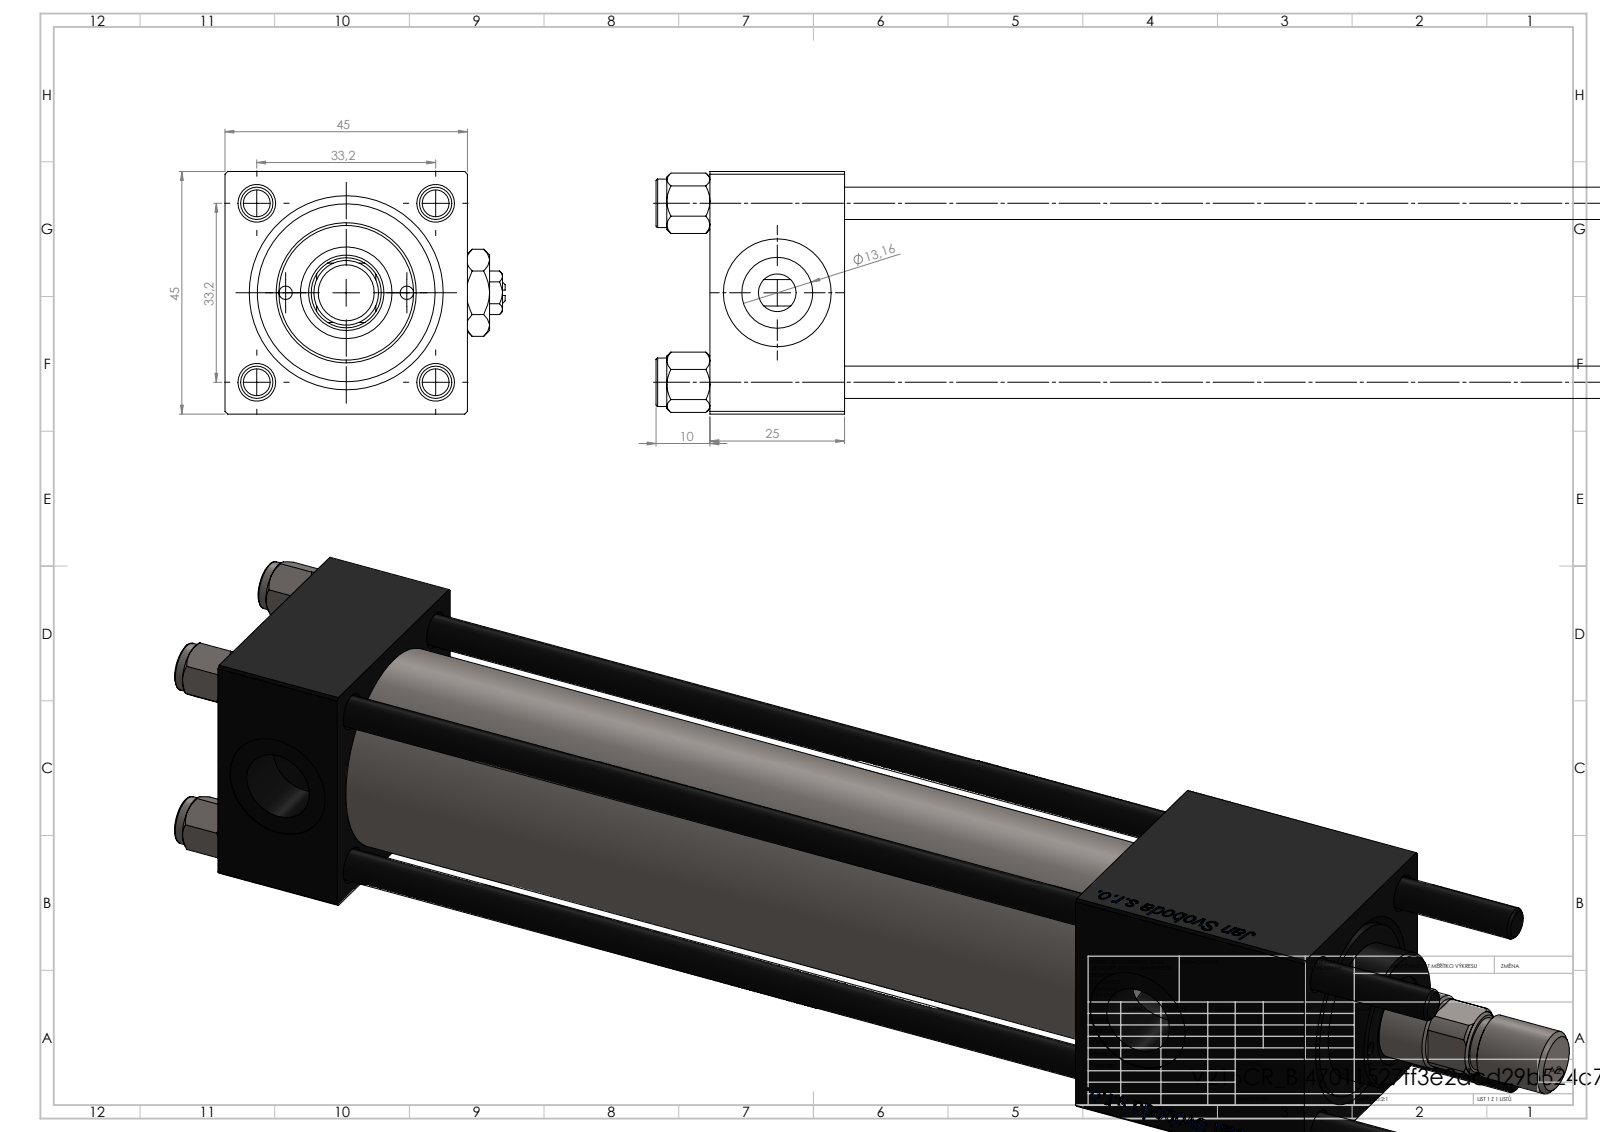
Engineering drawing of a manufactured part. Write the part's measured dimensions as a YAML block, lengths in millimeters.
part_name: "V215_VC_A; NUT_M5_B; V215CR_B-1; V215CR_B_TYCINKA (+3 more)"
step_written_by: "SolidWorks 2019 (CONFIG_CONTROL_DESIGN)"
units: millimeters
bodies: {solids: 13, faces: 1228, planar: 460, cylindrical: 92, other: 676}
overall_size: [279, 52, 45]
volume: 261796
surface_area: 110330
round_holes:
  - {diameter: 6, count: 4}
  - {diameter: 2.5, count: 2}
  - {diameter: 7, count: 2}
  - {diameter: 13.16, count: 2}
  - {diameter: 20, count: 2}
  - {diameter: 6.5, count: 1}
  - {diameter: 14, count: 1}
  - {diameter: 17, count: 1}
  - {diameter: 24, count: 1}
  - {diameter: 32, count: 1}
  - {diameter: 33, count: 1}
round_bosses_or_shafts:
  - {diameter: 9, count: 4}
  - {diameter: 38, count: 1}
  - {diameter: 26, count: 1}
  - {diameter: 12, count: 1}
  - {diameter: 10, count: 1}
partial_cylinders:
  - {radius: 6.5, count: 1}
face_to_face_distances: [45, 25, 228, 203, 180, 155, 48, 199.3, 174.3, 19.3]
hole_center_spacings: [17.44, 23.48, 32.42, 33.2, 11.25, 46.95, 22.5, 180.5]
